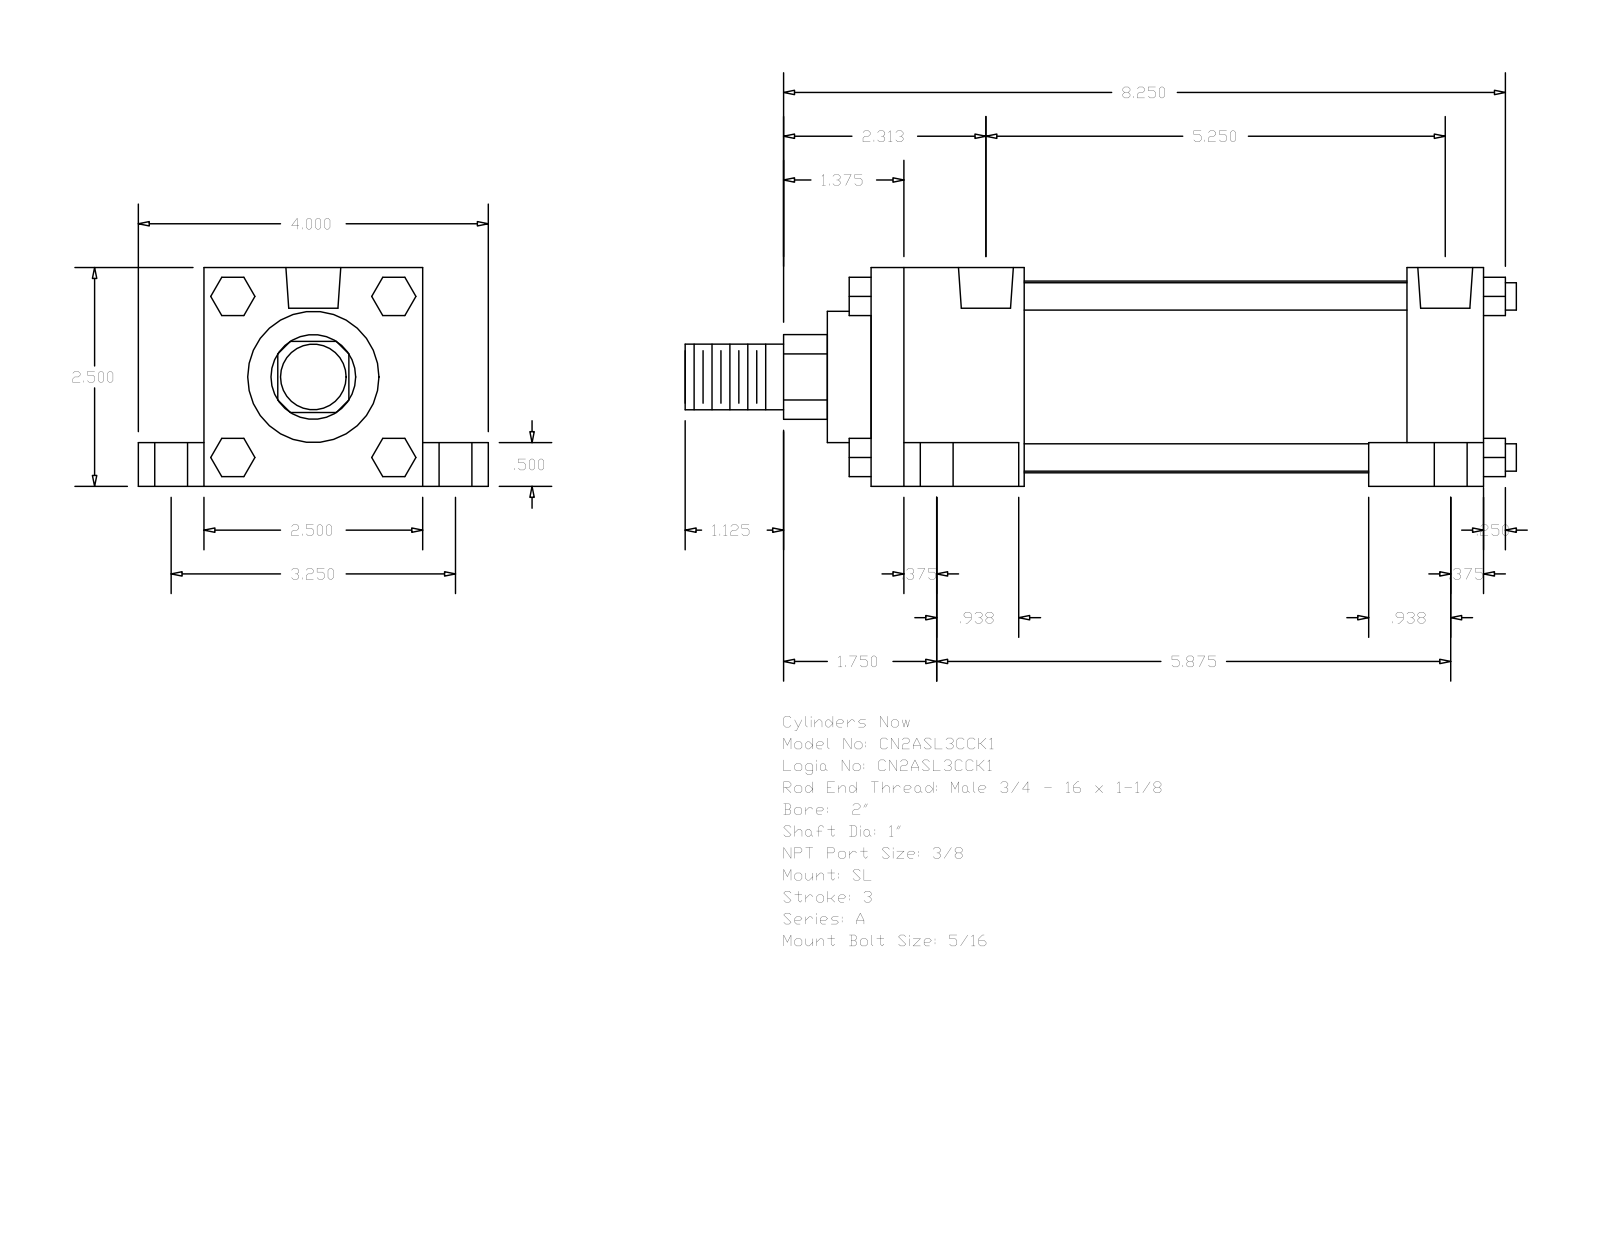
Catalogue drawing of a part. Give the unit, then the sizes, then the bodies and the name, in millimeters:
Units: millimetres
Overall size (bounding box): 241.3 × 101.6 × 63.5
Round holes (diameter × count): ⌀5.56 ×4, ⌀9.53 ×4, ⌀15.88 ×4, ⌀15.93 ×2
Round bosses / shafts (diameter × count): ⌀7.94 ×4, ⌀55.63 ×1, ⌀38.1 ×1, ⌀25.4 ×1, ⌀19.05 ×1
Partial cylindrical surfaces — rounded edges, fillets, slot ends (radius × count): R12.29 ×1
Main face-to-face distances: 63.5, 177.8, 12.7, 50.8, 19.05, 82.55, 44.45, 133.35, 155.57, 111.12
Hole centre spacings: 41.3, 41.64, 43.67, 44.22, 82.54, 127.78, 139.59, 141.11
Bodies: 0 solids, 148 faces (112 planar, 36 cylindrical, 0 other)
Part name (STEP PRODUCT): A_SL__0200_1
STEP written by: GSSL Pune (CONFIG_CONTROL_DESIGN)
